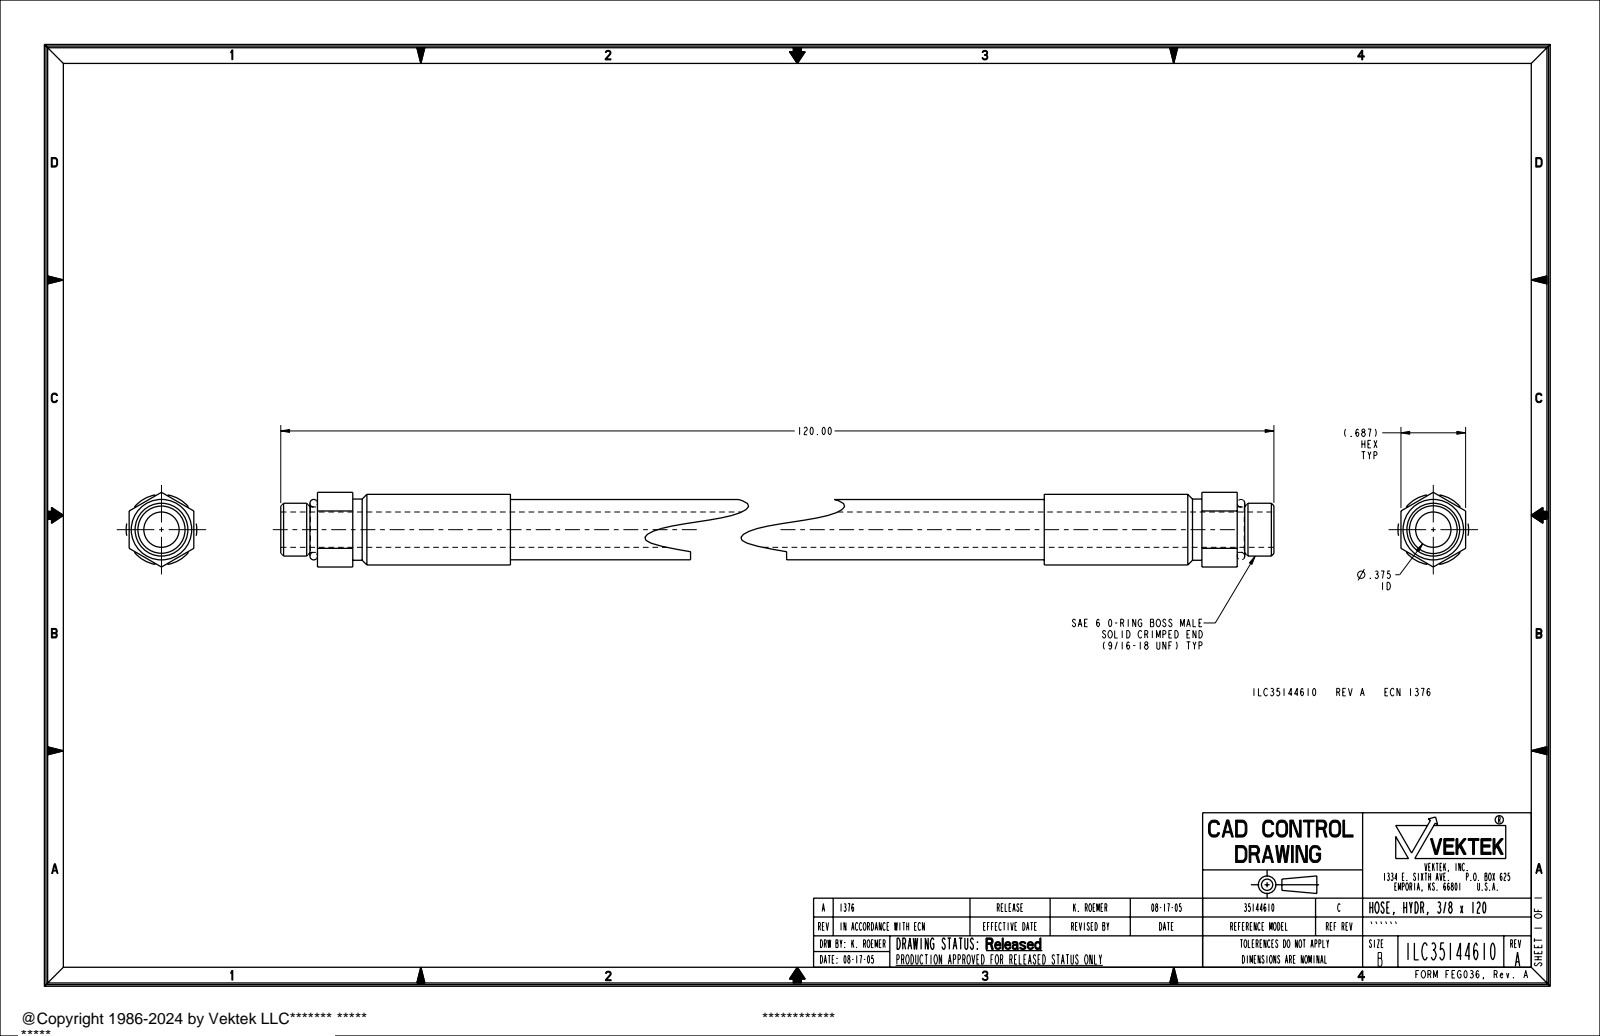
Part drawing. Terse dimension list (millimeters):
name: ILC35144610
written by: PRO/ENGINEER BY PARAMETRIC TECHNOLOGY CORPORATION, 2004290 (AUTOMOTIVE_DESIGN_CC2)
unit: mm
bodies: 3 solids, 60 faces (20 planar, 20 cylindrical, 20 other)
size: 3048 × 20.1 × 19.1
volume: 421 800 mm³; area: 249 000 mm²
holes: 1× ⌀9.5
bosses: 1× ⌀19.1, 1× ⌀16.5, 1× ⌀16.3, 1× ⌀14.2, 1× ⌀12.2
face distances: 17.4, 52.1, 2976.1, 3028.2, 9.9, 62, 2986, 3038.1, 19.4, 3028.6
